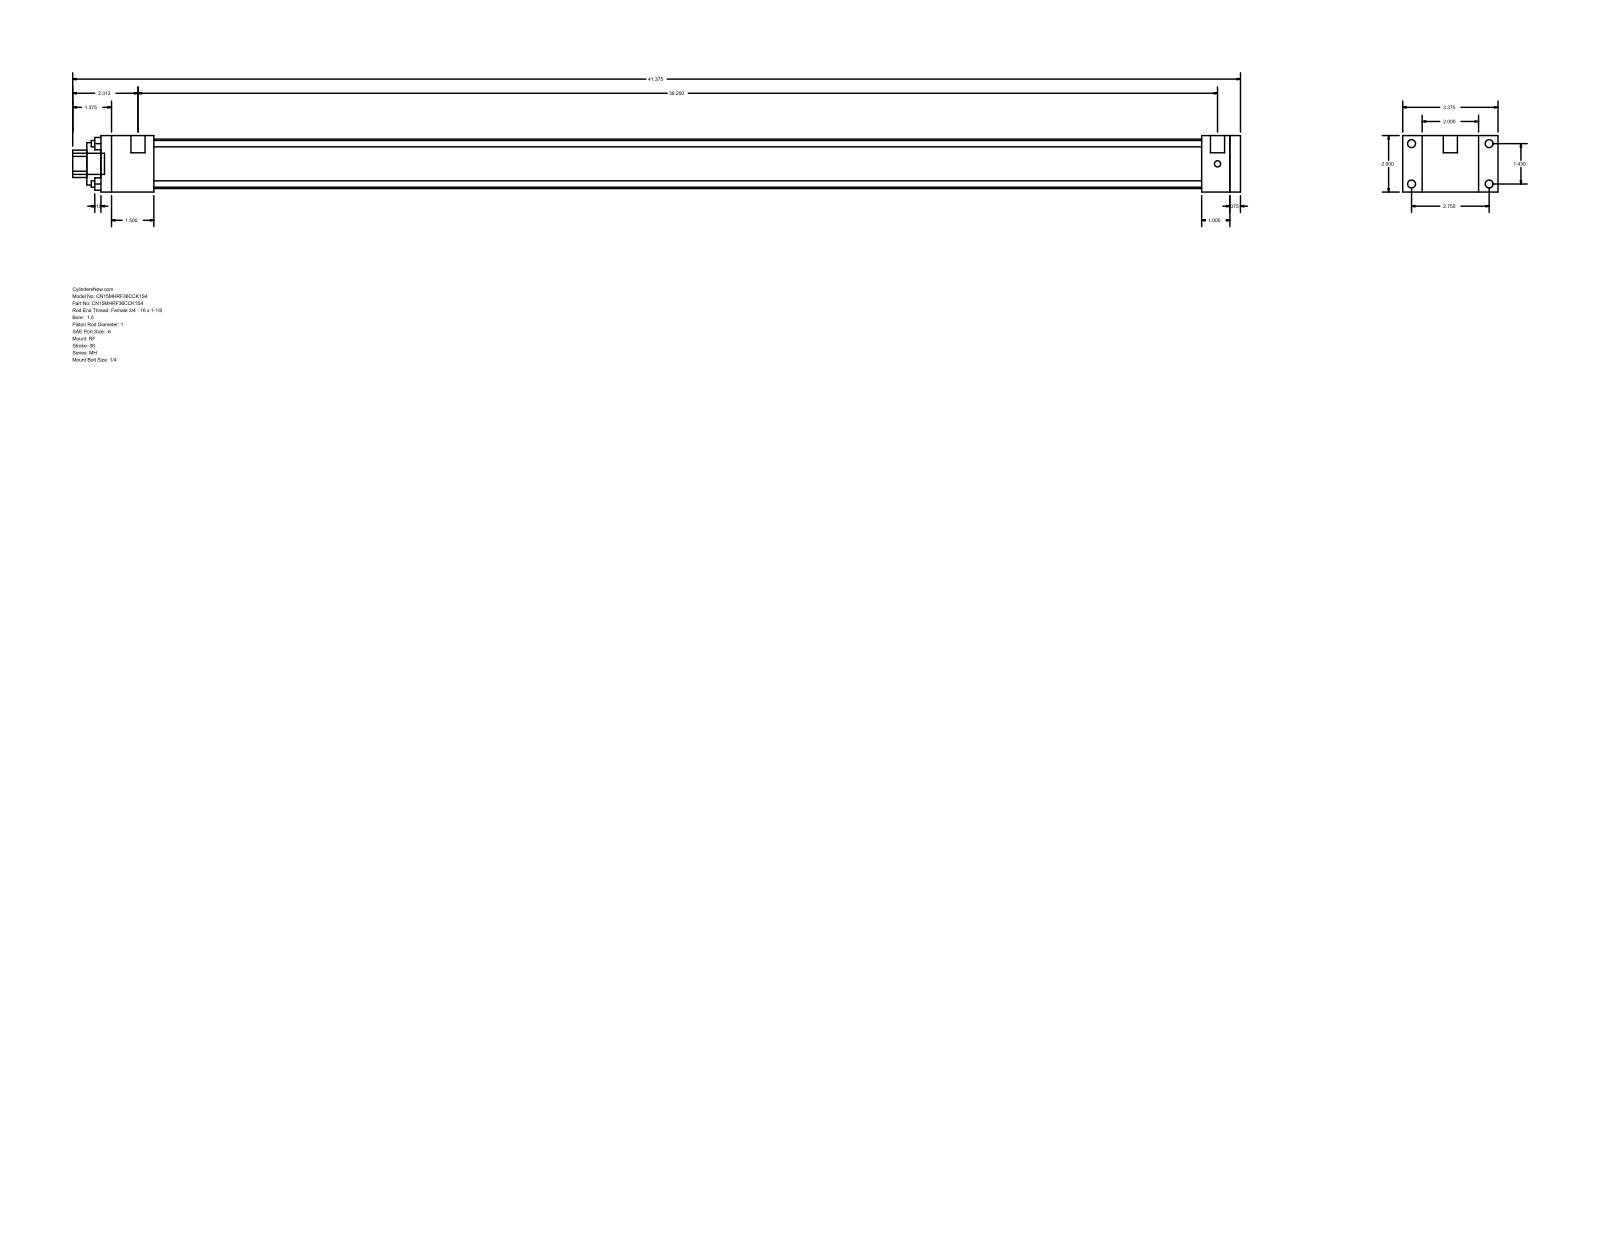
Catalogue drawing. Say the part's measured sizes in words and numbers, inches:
The part is named "MH_RF__0150_1". Its 3-D file was written by "GSSL Pune (CONFIG_CONTROL_DESIGN)". It is 0 solids with 92 faces: 64 planar, 28 cylindrical and 0 other. Overall it measures 41.375 by 3.375 by 2 inches. Round holes: 4 of diameter 0.225, 1 of diameter 1, 1 of diameter 1.5, 1 of diameter 1.75. Round bosses or shafts: 4 of diameter 0.281, 4 of diameter 0.219, 2 of diameter 0.5, 1 of diameter 0.75. Partial cylindrical surfaces (rounded edges, fillets, slot ends): 1 of radius 0.484. The main face-to-face distances are 2, 0.375, 40, 1, 40.375, 0.687, 2.687, 39, 1.375, 1.875. The hole center spacings are 1.011, 1.43, 2.022.
